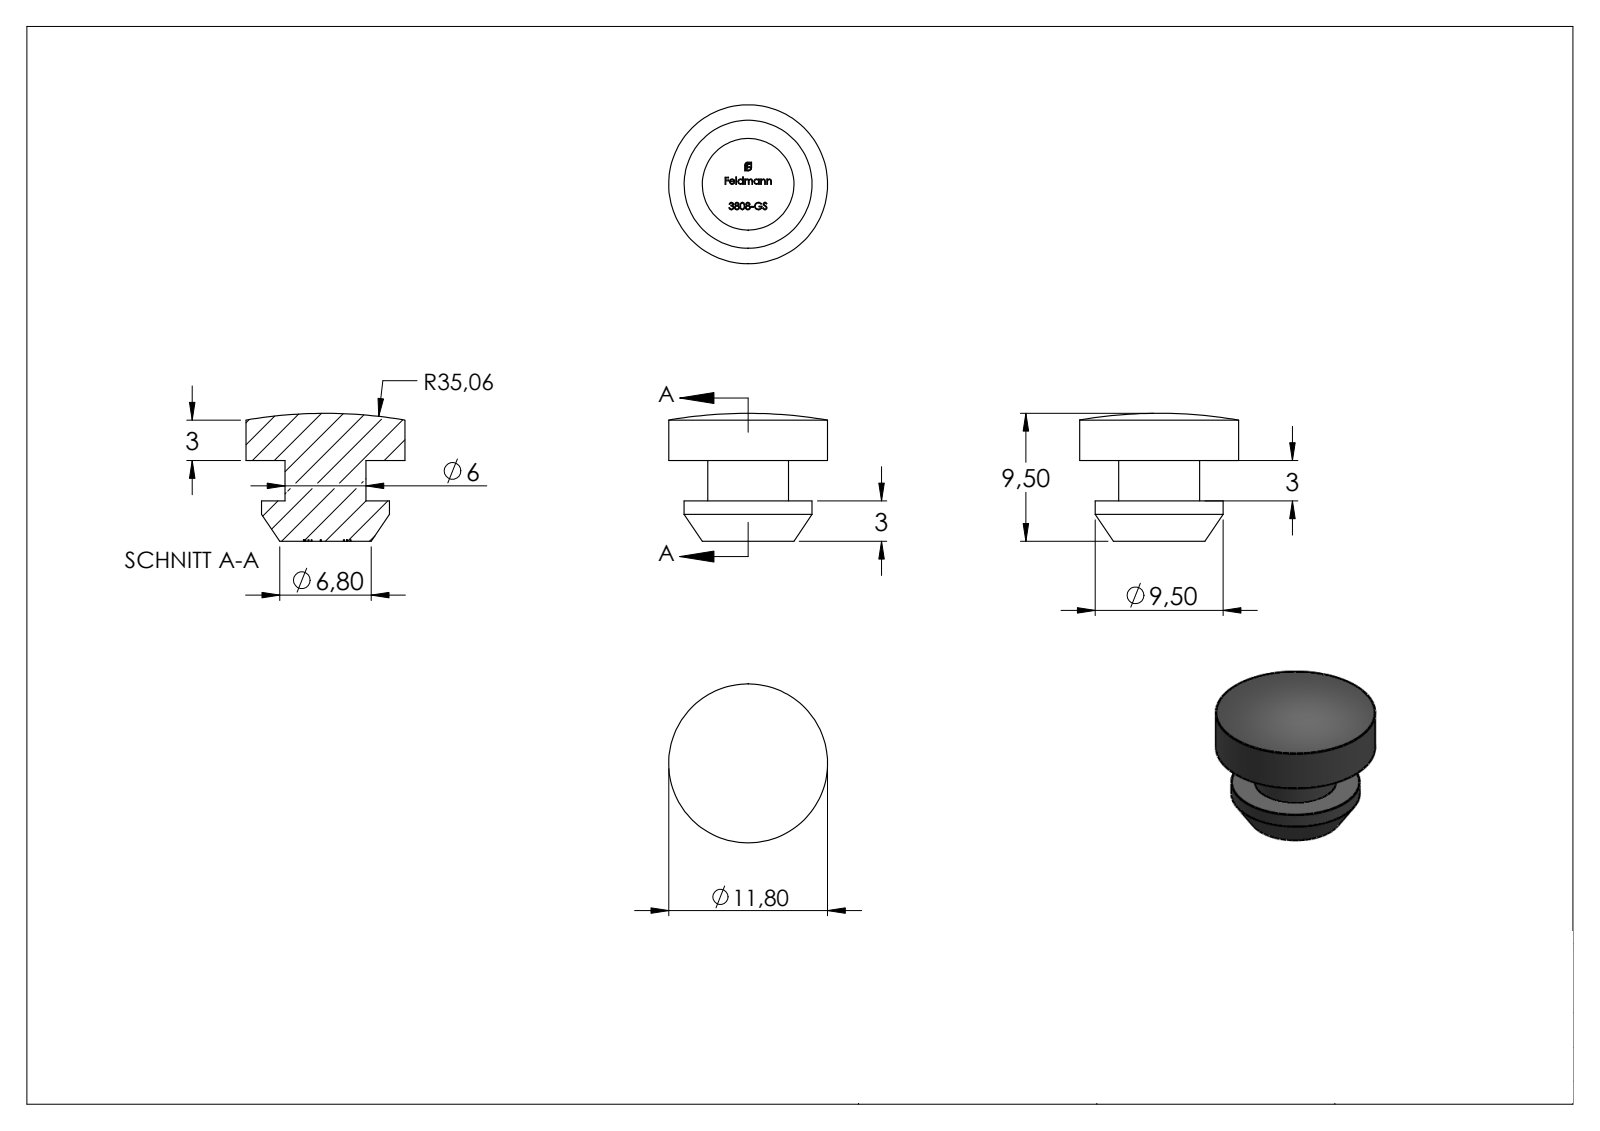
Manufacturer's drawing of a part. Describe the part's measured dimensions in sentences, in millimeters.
The part is named "3808-GS". Its 3-D file was written by "SolidWorks 2018 (CONFIG_CONTROL_DESIGN)". It is 1 solid with 273 faces: 114 planar, 6 cylindrical and 153 other. Overall it measures 11.8 by 11.8 by 9.5 millimeters. Its volume is 616 cubic millimeters and its surface area 534 square millimeters. Round bosses or shafts: 1 of diameter 11.8, 1 of diameter 9.5, 1 of diameter 6. The main face-to-face distances are 3, 6, 2.9, 5.9, 1.19, 0.66, 0.61, 1.11, 0.45, 0.5.
